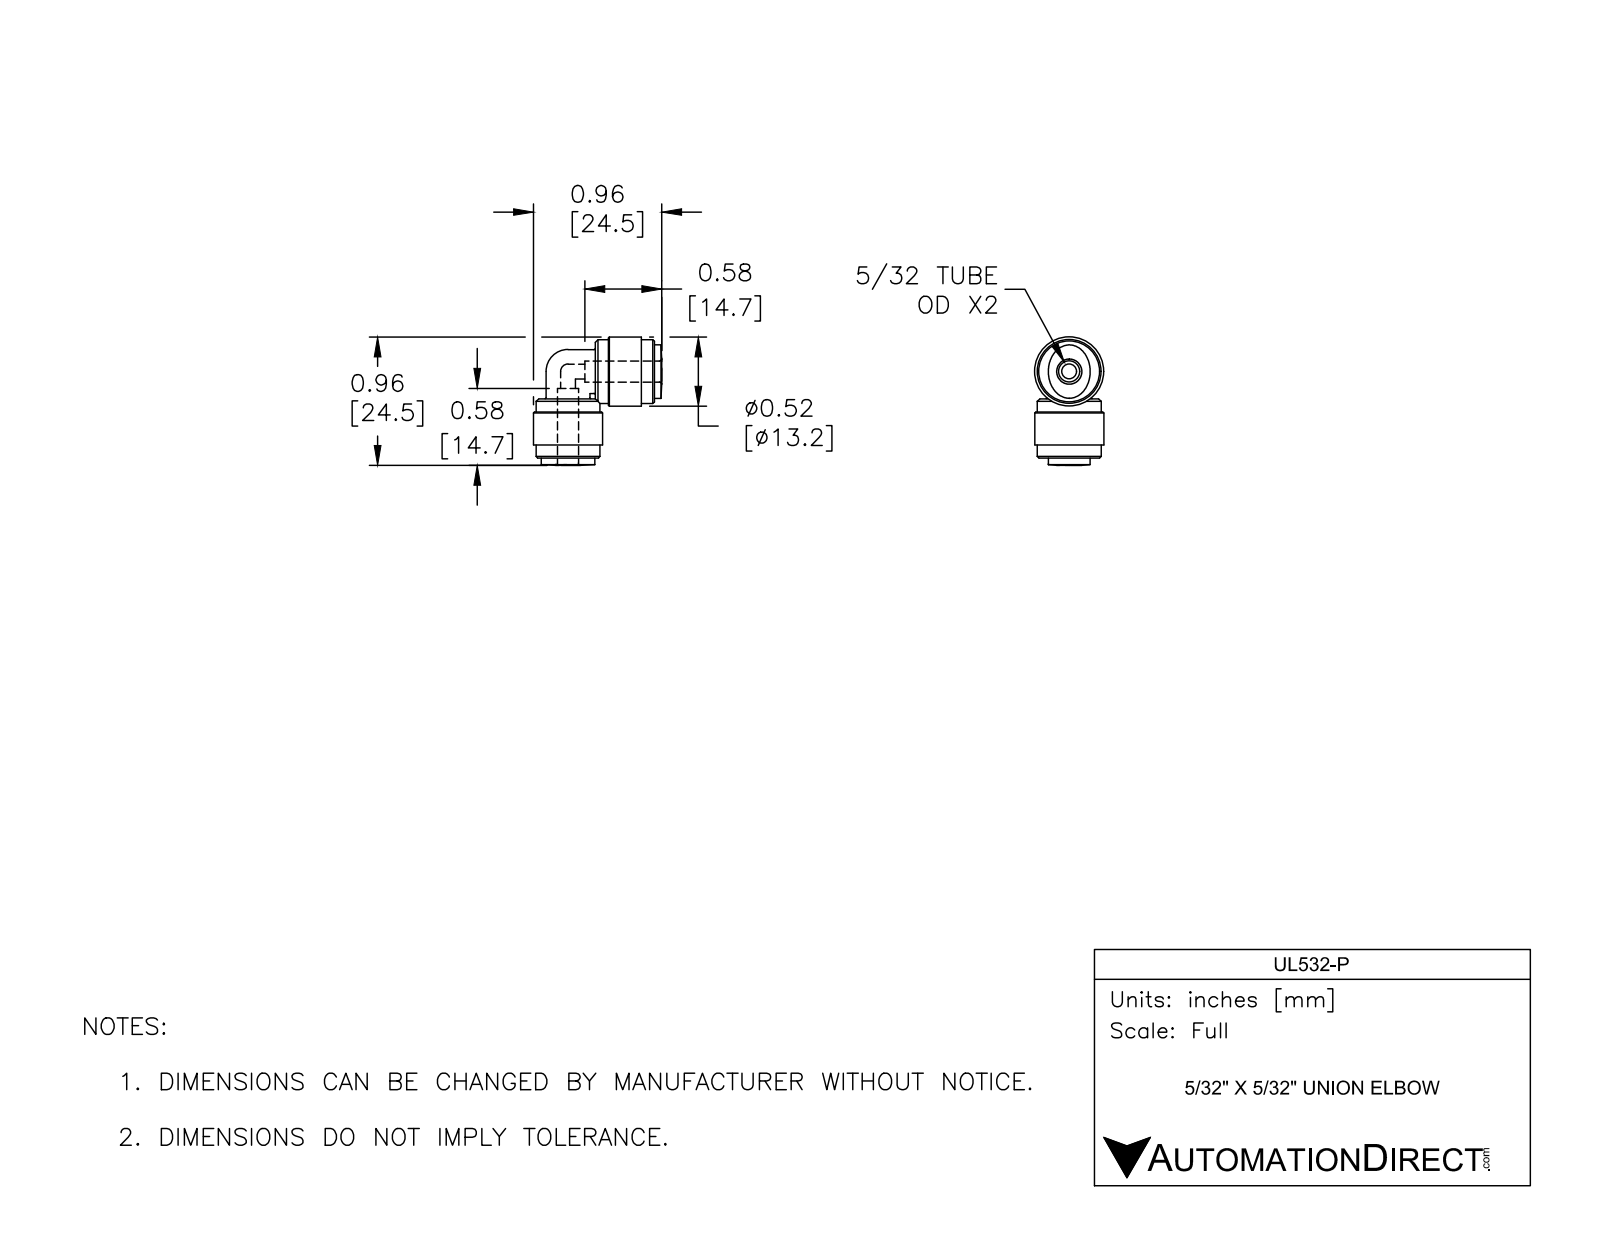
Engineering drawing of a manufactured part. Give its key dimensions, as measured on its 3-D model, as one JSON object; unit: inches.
{"part_name": "UL532-P", "step_written_by": "SolidWorks 2017 (AUTOMOTIVE_DESIGN)", "units": "inches", "bodies": {"solids": 1, "faces": 67, "planar": 10, "cylindrical": 24, "other": 33}, "overall_size": [0.965, 0.965, 0.52], "volume_in3": 0.195, "surface_area_in2": 3.13, "round_holes": [[0.11, 2], [0.157, 2]], "round_bosses_or_shafts": [[0.52, 2], [0.48, 2], [0.331, 2]], "face_to_face_distances": [0.445, 0.098, 0.346, 0.248, 0.524, 0.425, 0.177, 0.079]}
